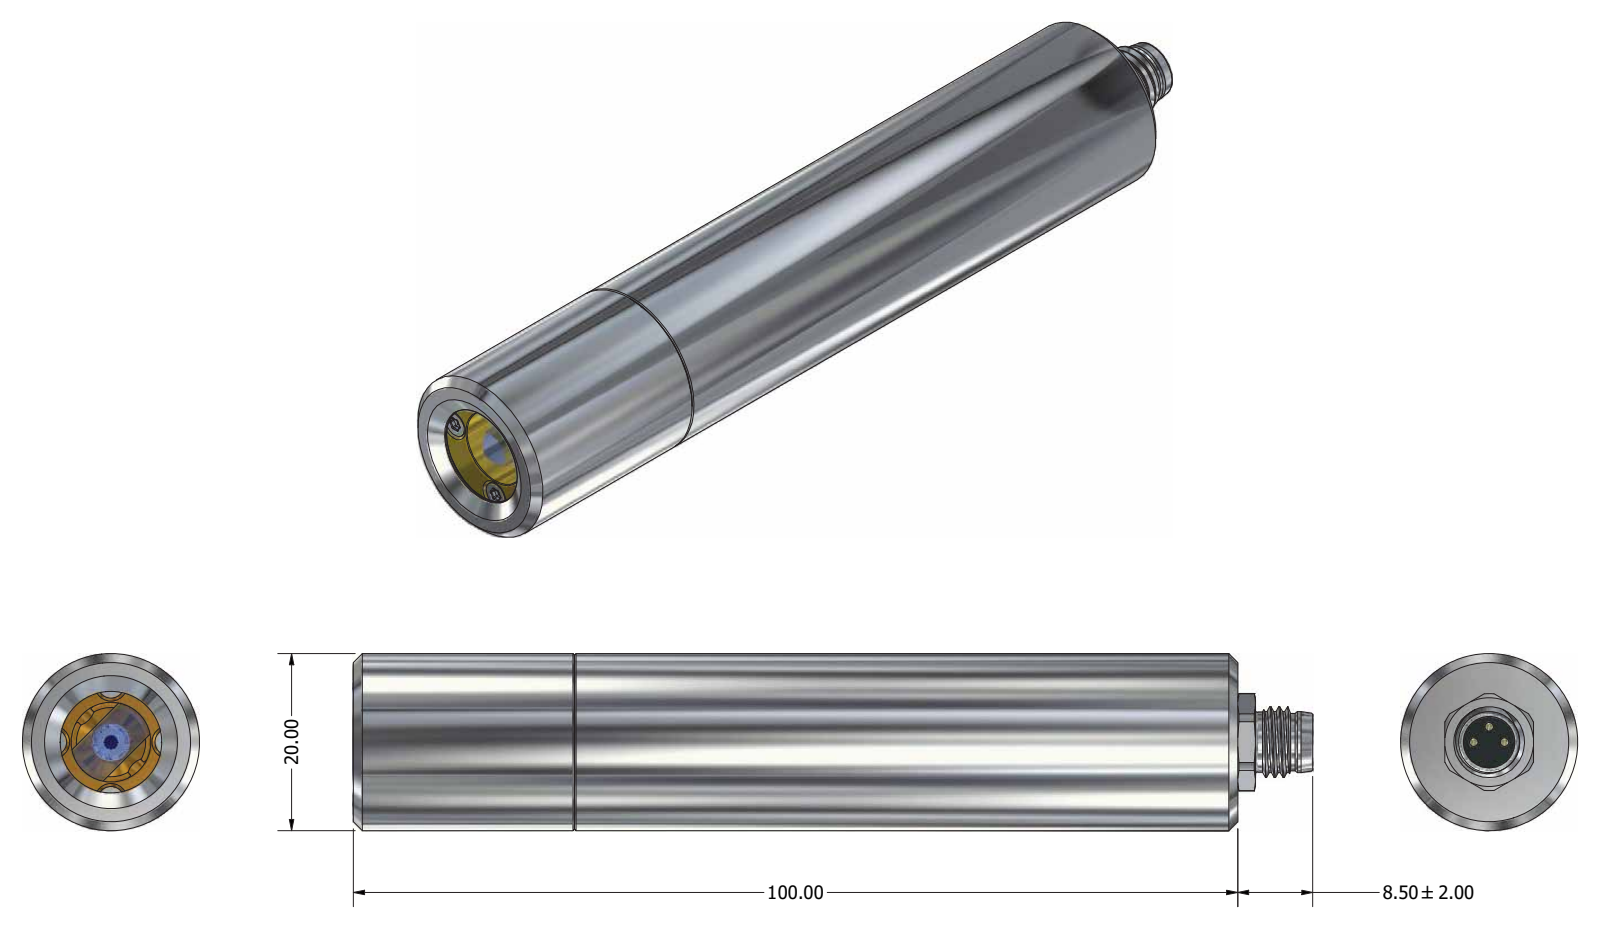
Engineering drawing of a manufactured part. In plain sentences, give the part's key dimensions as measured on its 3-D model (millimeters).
The part is named "lwpro_v10; back_v9; front_v9; m8-3p_realthread". Its 3-D file was written by "unknown (AUTOMOTIVE_DESIGN)". It is 3 solids with 223 faces: 41 planar, 60 cylindrical and 122 other. Overall it measures 108.5 by 20 by 20 millimeters. Its volume is 15 576 cubic millimeters and its surface area 12 361 square millimeters. Round holes: 1 of diameter 5.8, 1 of diameter 7.46, 1 of diameter 11.5, 1 of diameter 13, 1 of diameter 16.1, 1 of diameter 17.46, 1 of diameter 18, 1 of diameter 18.4. Round bosses or shafts: 3 of diameter 1.05, 3 of diameter 1, 3 of diameter 0.6, 1 of diameter 20, 1 of diameter 8, 1 of diameter 7.2, 1 of diameter 6.9, 1 of diameter 6.8. Partial cylindrical surfaces (rounded edges, fillets, slot ends): 1 of radius 3.96, 1 of radius 5.5. The main face-to-face distances are 100, 5, 98.6, 1.4, 2, 75, 23.6, 25, 8.5, 10.
